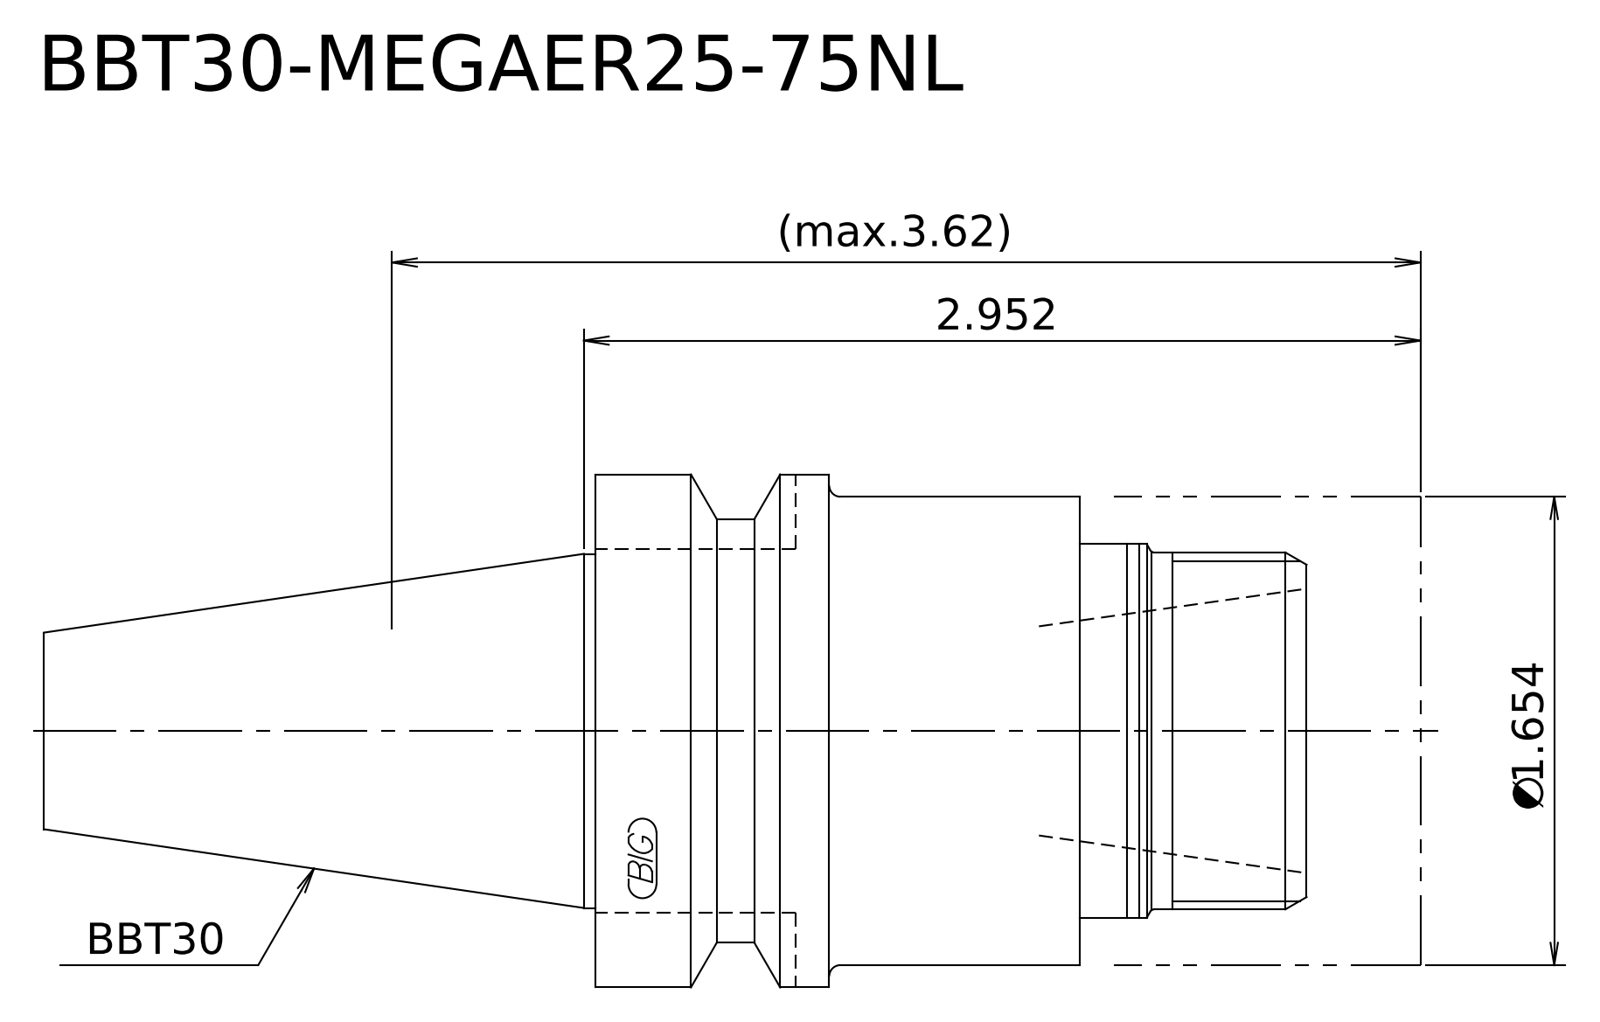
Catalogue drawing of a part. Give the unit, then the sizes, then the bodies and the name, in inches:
Units: inches
Overall size (bounding box): 4.858 × 1.811 × 1.811
Round bosses / shafts (diameter × count): ⌀1.811 ×1, ⌀1.654 ×1, ⌀1.496 ×1, ⌀1.319 ×1, ⌀1.26 ×1, ⌀1.25 ×1
Main face-to-face distances: 1.083, 2.913, 1.831, 0.402, 0.681, 2.512, 1.201, 0.799, 0.118, 1.713
Volume: 8.696 in³ · Surface area: 33.19 in²
Bodies: 2 solids, 21 faces (7 planar, 8 cylindrical, 6 other)
STEP written by: Kubotek KeyCreator 2011 V10.0.2 (22737) (automotive_design)
